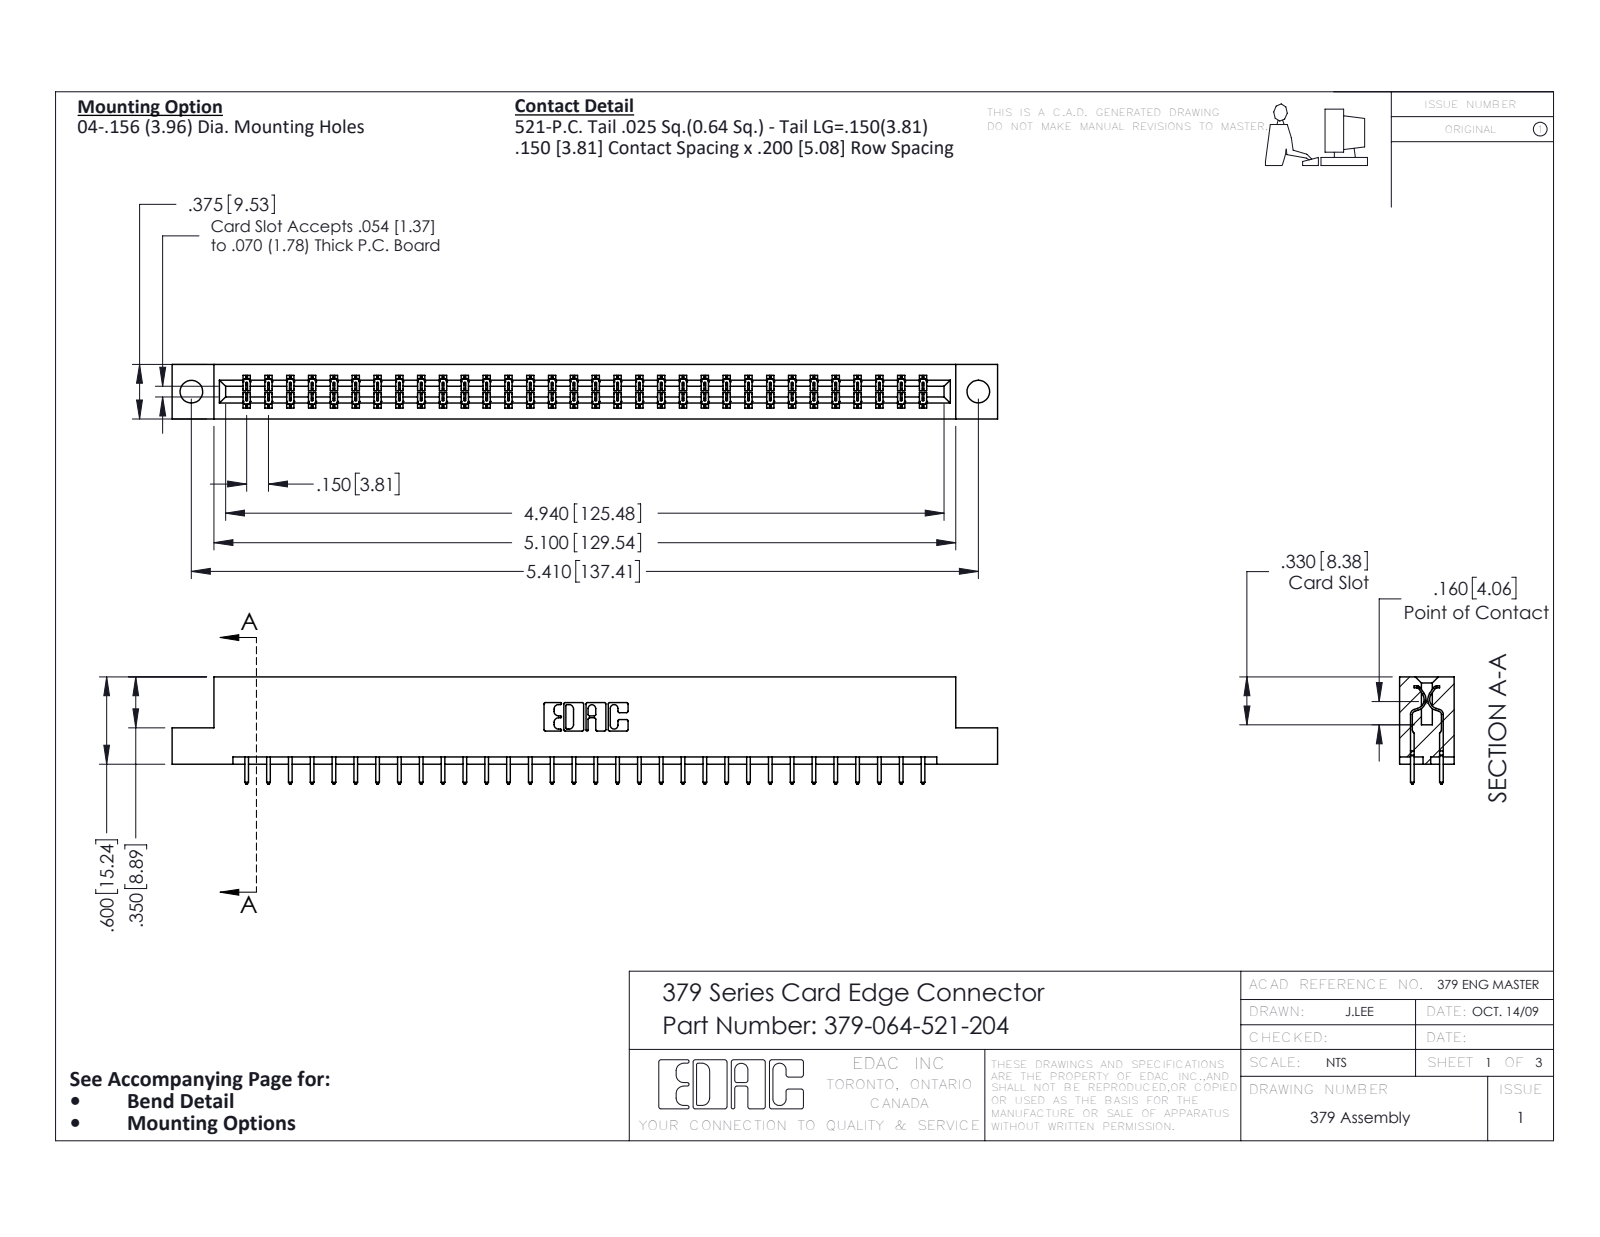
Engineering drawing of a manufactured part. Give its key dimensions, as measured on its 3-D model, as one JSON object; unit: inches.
{"part_name": "379-064-521-204; 379 Part_Flush - .156 Dia - TH; 345-292-001_345-293-121", "step_written_by": "SolidWorks 2016 (CONFIG_CONTROL_DESIGN)", "units": "inches", "bodies": {"solids": 65, "faces": 3442, "planar": 2374, "cylindrical": 1068, "other": 0}, "overall_size": [5.675, 0.737, 0.375], "volume_in3": 0.923, "surface_area_in2": 25.57, "round_holes": [[0.156, 2]], "partial_cylinders_radius": [[0.006, 96], [0.01, 64], [0.01, 22], [0.007, 6], [0.031, 6], [0.026, 3], [0.014, 2], [0.022, 2]], "face_to_face_distances": [0.3, 0.075, 0.375, 0.2, 0.1, 0.225, 0.15, 0.076, 0.275, 0.025], "hole_center_spacings": [5.41]}
